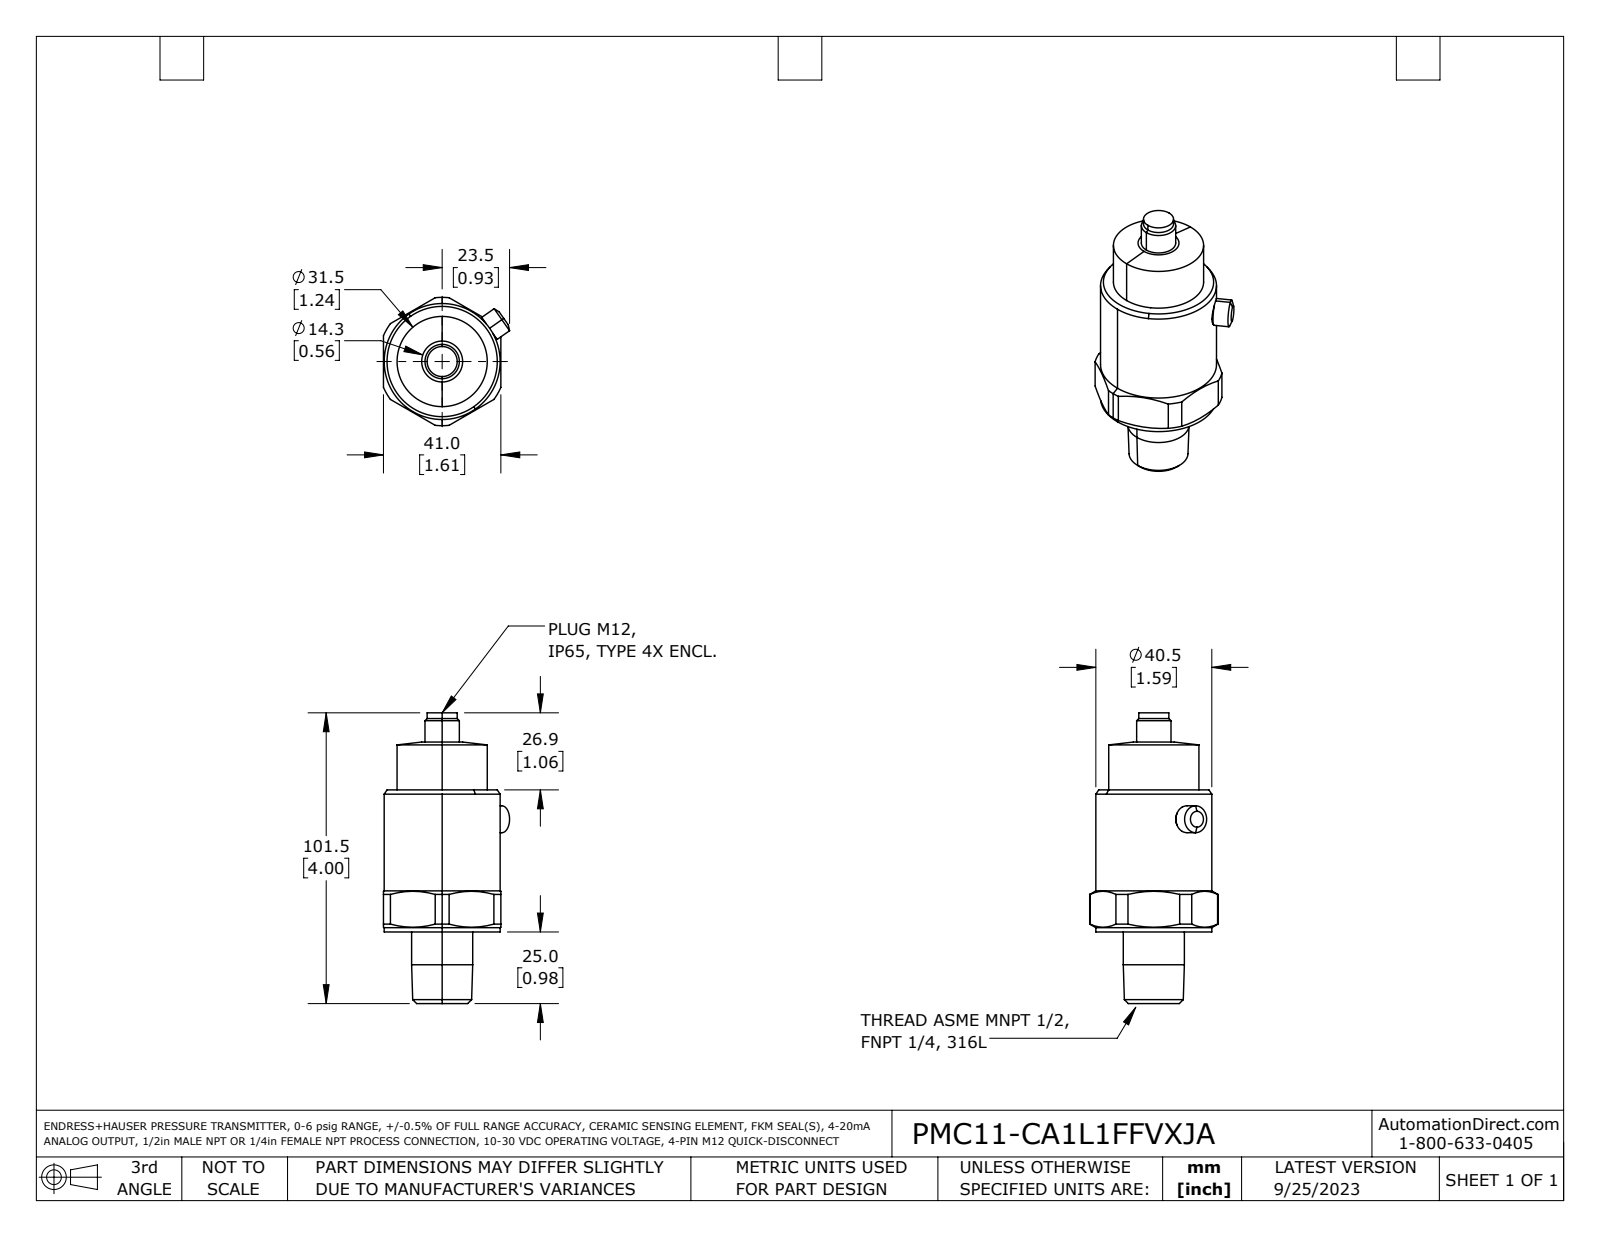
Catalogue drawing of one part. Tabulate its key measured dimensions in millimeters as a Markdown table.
| quantity | value |
| --- | --- |
| part name | PMC11-CA1L1FFVXJA |
| STEP written by | SolidWorks 2021 (AUTOMOTIVE_DESIGN) |
| units | millimeters |
| bodies | 1 solid, 65 faces (15 planar, 28 cylindrical, 22 other) |
| overall size | 101.5 × 44.8 × 44 |
| volume | 86 970 mm³ |
| surface area | 13 300 mm² |
| round holes (diameter × count) | 9 × 1 |
| round bosses / shafts (diameter × count) | 40.5 × 1, 31.5 × 1, 21.3 × 1, 12 × 1, 10.5 × 1, 9.4 × 1, 8.5 × 1 |
| partial cylindrical surfaces (radius × count) | 22.4 × 1 |
| main face-to-face distances | 41, 49.6, 25, 74.6, 101.5, 76.5, 26.9, 15.5, 9.5, 59.1 |
